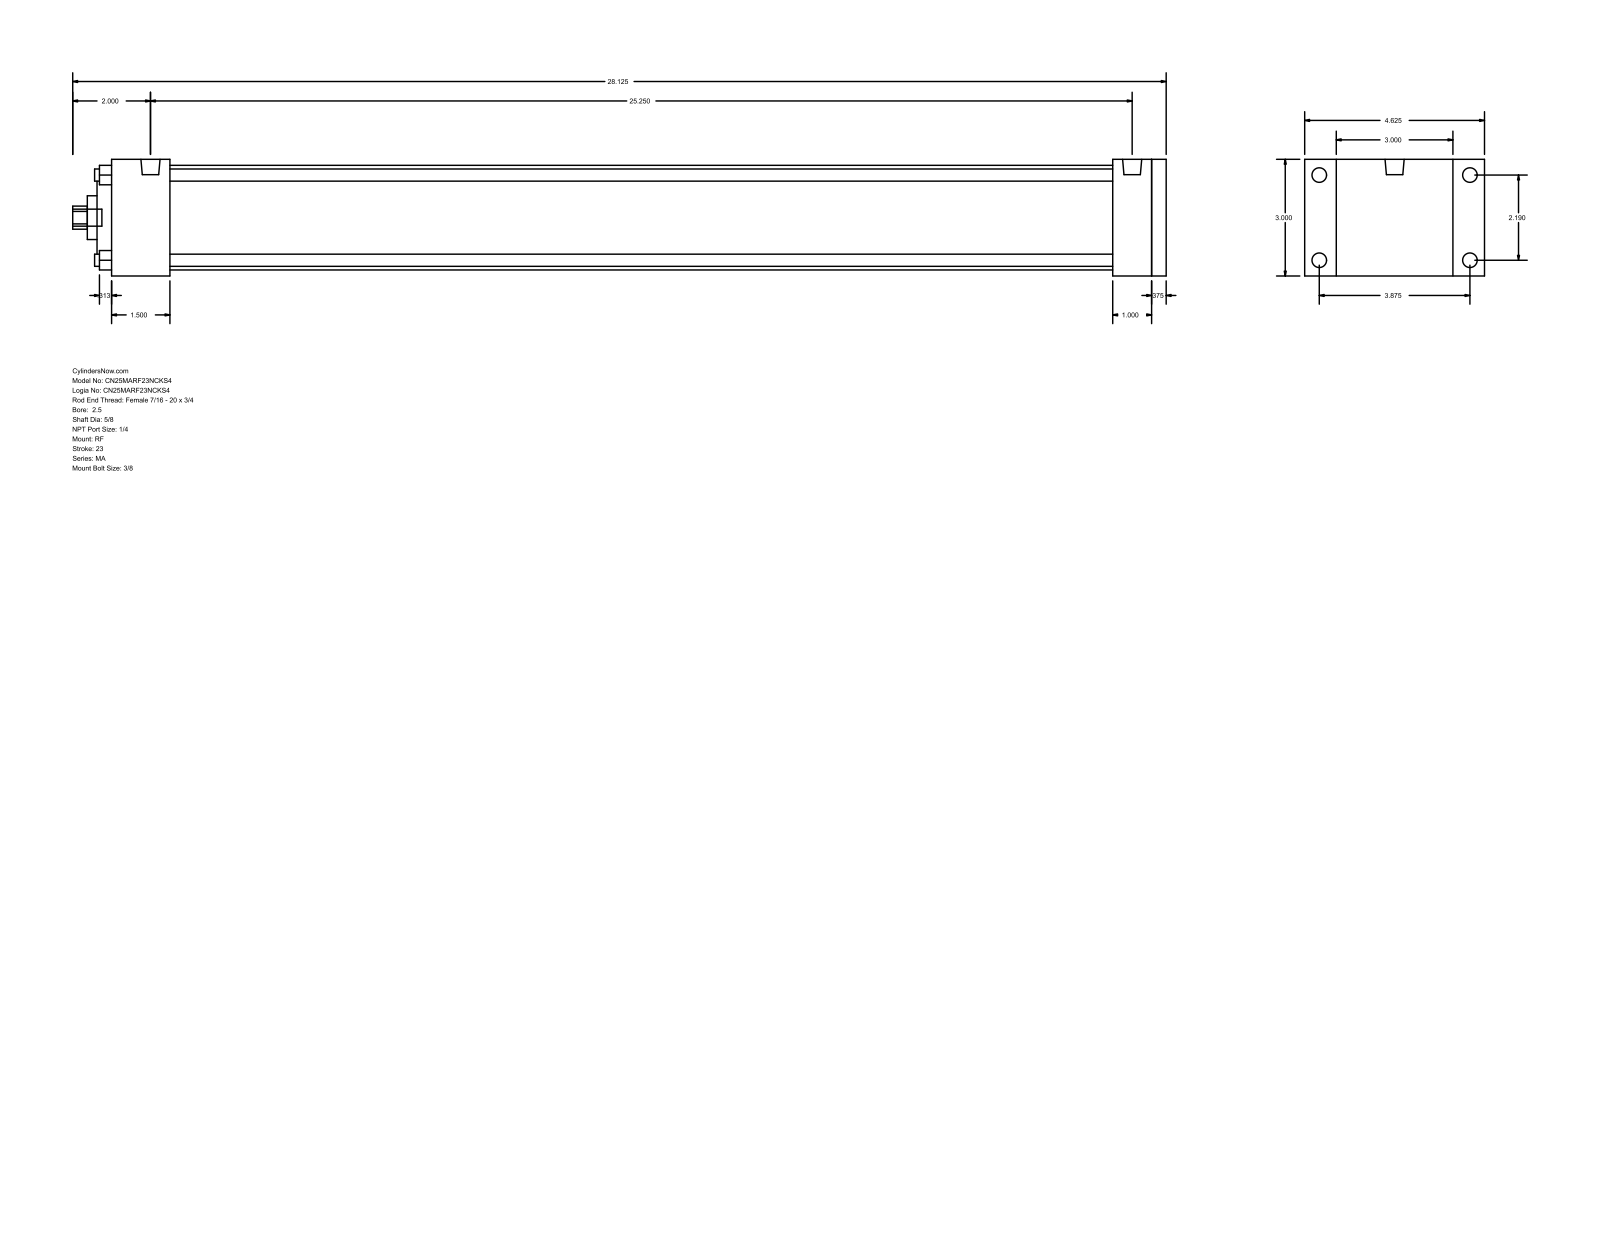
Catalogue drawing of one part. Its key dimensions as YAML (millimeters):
part_name: "MA_RF__0250_0.625"
step_written_by: "GSSL Pune (CONFIG_CONTROL_DESIGN)"
units: millimeters
bodies: {solids: 0, faces: 94, planar: 65, cylindrical: 29, other: 0}
overall_size: [714.38, 117.47, 76.2]
round_holes:
  - {diameter: 7.94, count: 4}
  - {diameter: 15.88, count: 1}
  - {diameter: 28.57, count: 1}
  - {diameter: 50.8, count: 1}
  - {diameter: 68.33, count: 1}
round_bosses_or_shafts:
  - {diameter: 9.53, count: 4}
  - {diameter: 7.94, count: 4}
  - {diameter: 12.49, count: 2}
  - {diameter: 11.11, count: 1}
partial_cylinders:
  - {radius: 7.54, count: 1}
face_to_face_distances: [76.2, 688.98, 9.53, 679.45, 25.4, 38.1, 654.05, 615.95, 641.35, 650.88]
hole_center_spacings: [39.33, 55.62, 78.66]
